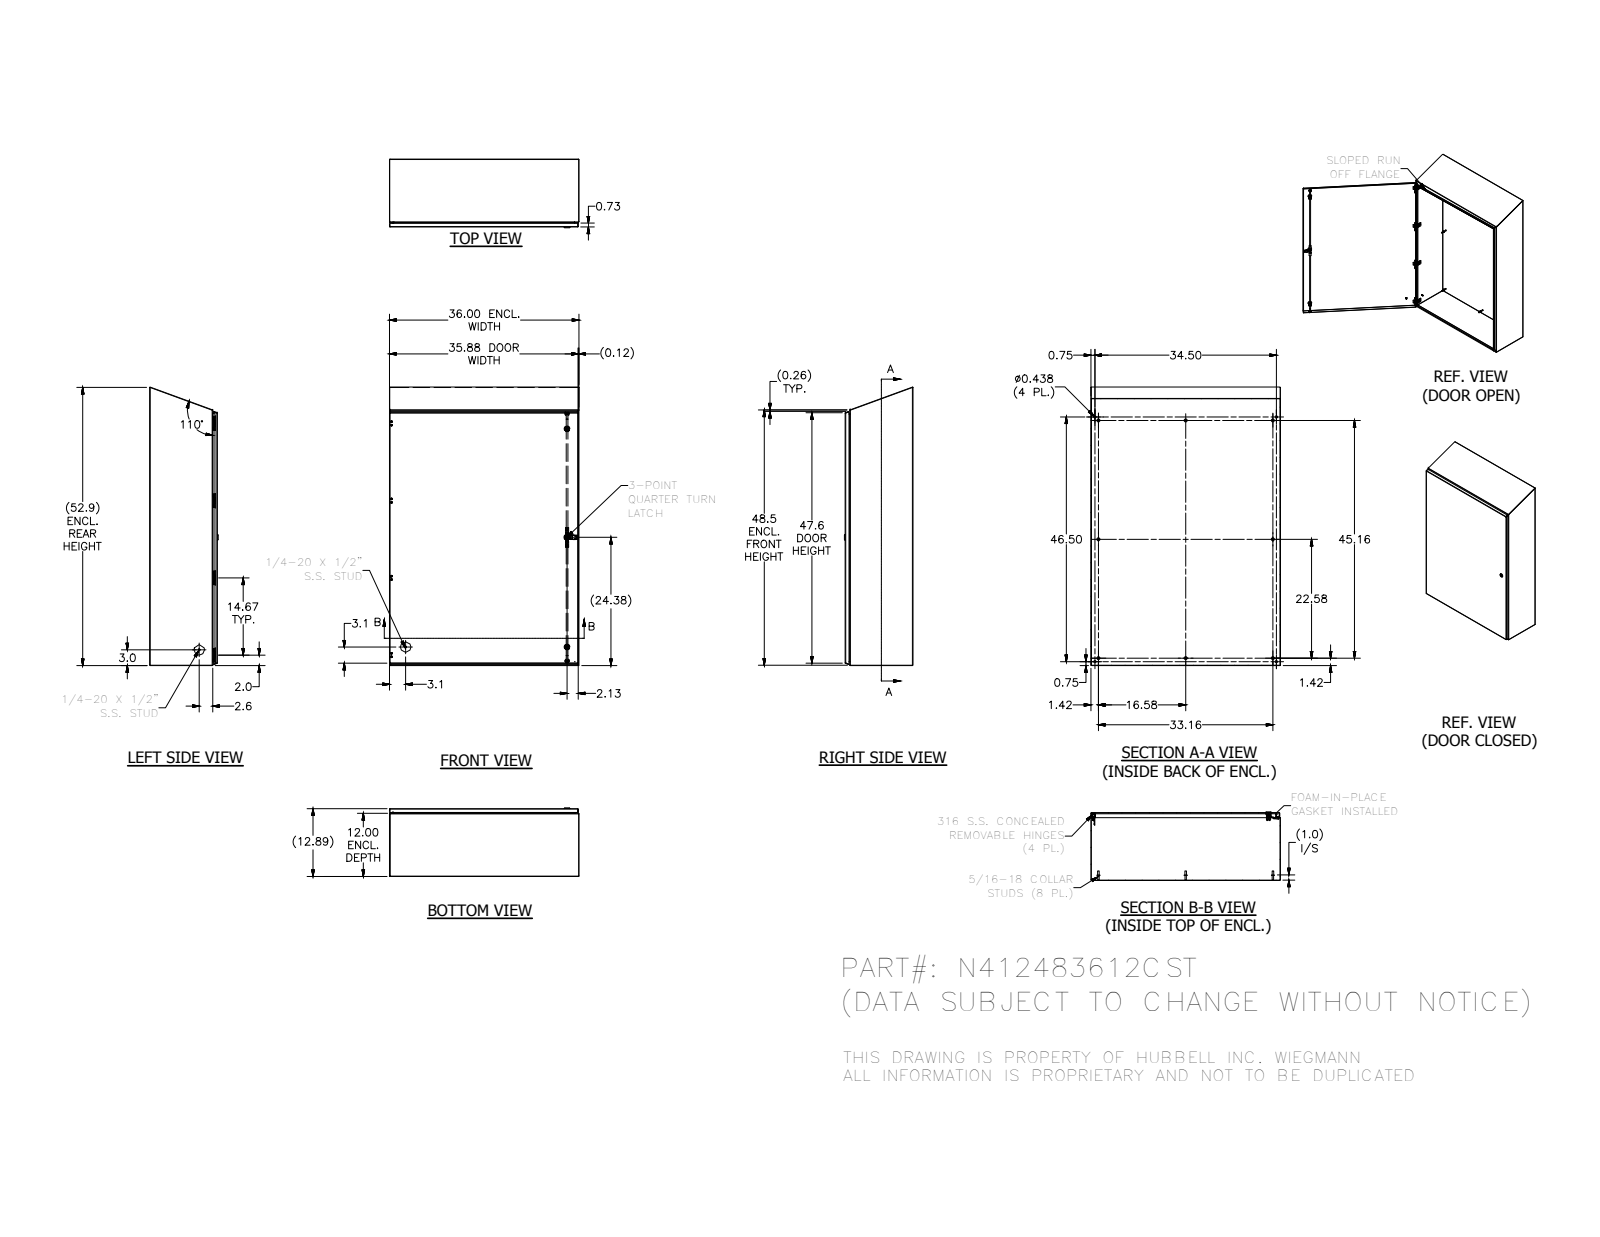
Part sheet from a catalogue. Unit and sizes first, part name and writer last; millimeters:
Units: millimetres
Overall size (bounding box): 1344.2 × 914.4 × 331.3
Round holes (diameter × count): ⌀2.4 ×8, ⌀3.9 ×8, ⌀4.2 ×8, ⌀4.4 ×8, ⌀4.7 ×8, ⌀4 ×5, ⌀4.2 ×4, ⌀5 ×4, ⌀11.1 ×4, ⌀2.7 ×2, ⌀4.1 ×2, ⌀4.3 ×2
Round bosses / shafts (diameter × count): ⌀6.4 ×18, ⌀14.3 ×8, ⌀9.1 ×8, ⌀8.1 ×8, ⌀7.6 ×8, ⌀7 ×8, ⌀6.5 ×8, ⌀4.2 ×8
Partial cylindrical surfaces — rounded edges, fillets, slot ends (radius × count): R1.3 ×50, R0.8 ×36, R0.4 ×34, R3.2 ×32, R0.3 ×31, R0.5 ×20, R2.7 ×18, R0.8 ×16
Main face-to-face distances: 1.9, 325.5, 323.6, 327.3, 912.5, 910.6, 914.4, 302.9, 22.5, 20.7
Hole centre spacings: 372.5, 745.1, 372.5, 1117.6, 12.7, 16.7, 33.2, 372.7
Volume: 7 463 000 mm³ · Surface area: 7 935 000 mm²
Bodies: 79 solids, 2617 faces (954 planar, 979 cylindrical, 684 other)
Part name (STEP PRODUCT): N412_CST-assm3pcblr; N412483612CSTBLR; HFW3161; HFW328176 (+8 more)
STEP written by: Autodesk Inventor 2012 (AUTOMOTIVE_DESIGN)
